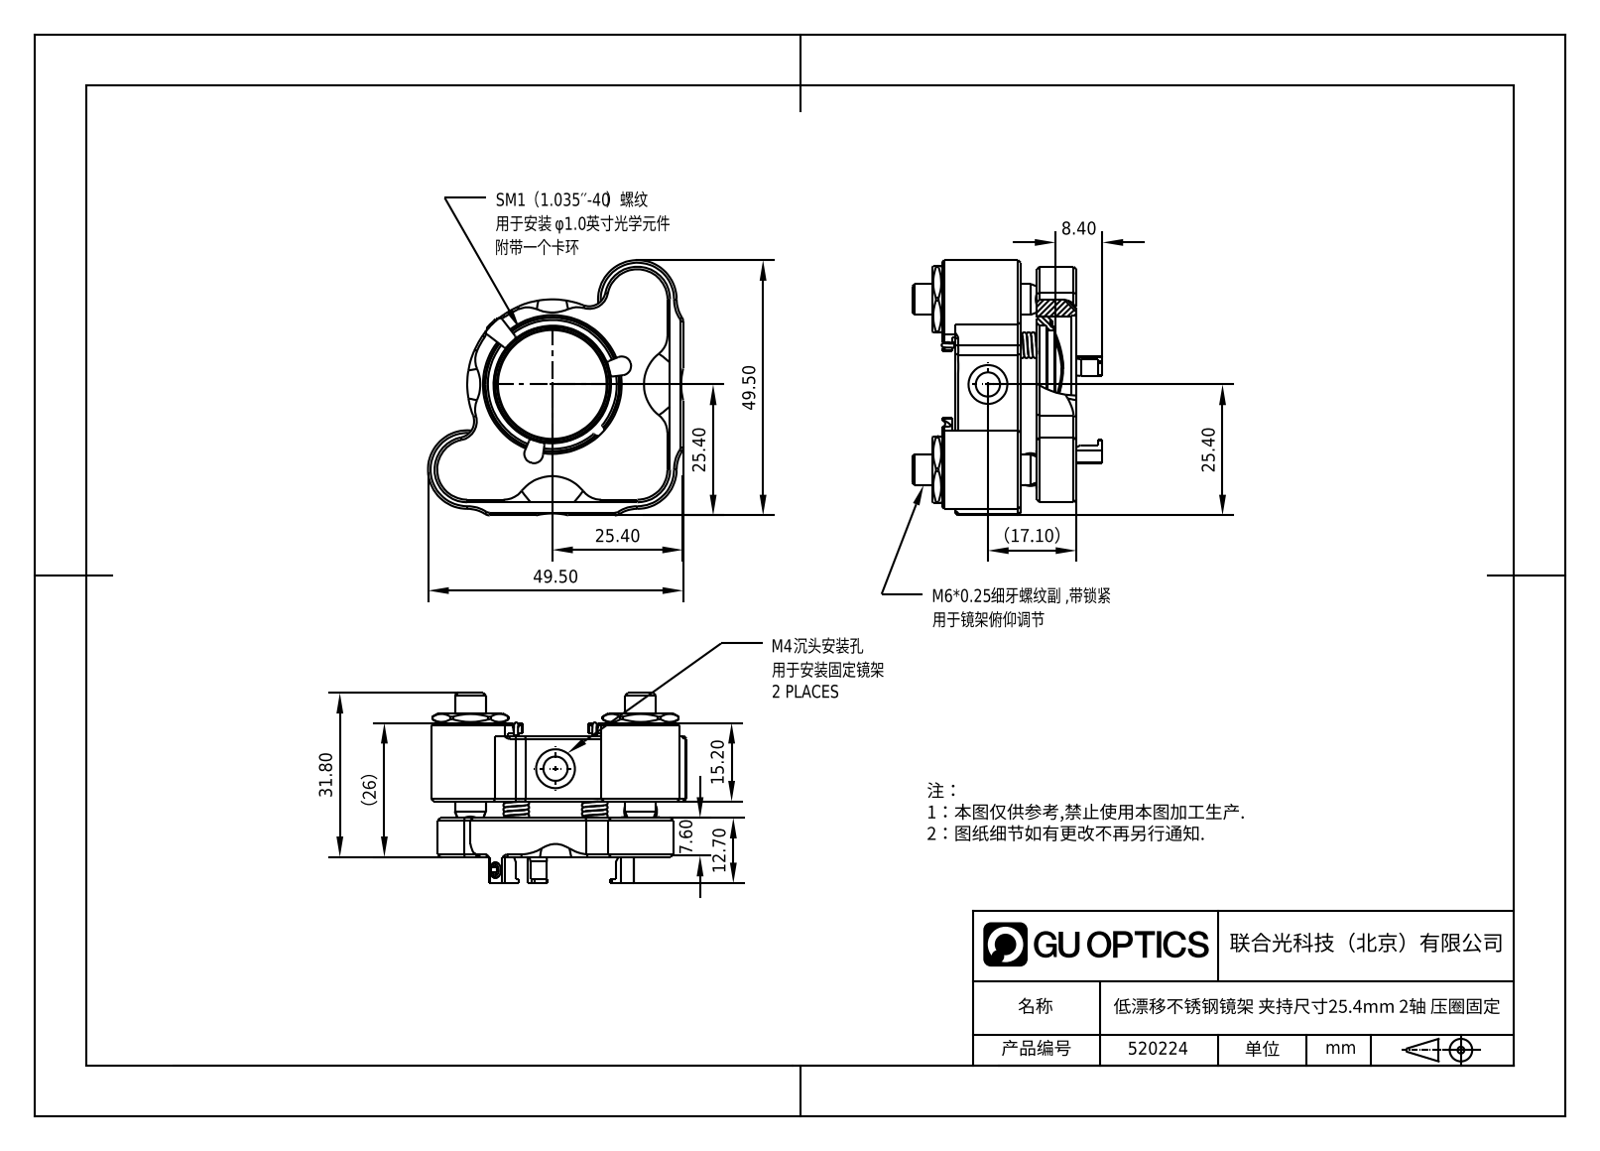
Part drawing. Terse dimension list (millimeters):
name: DXS-0625标准型细牙螺丝_3.2.2.16-DXS-0625-26.6; 1.1.20.26.1_替代进口不锈钢光学调整架前面板，低变形，SM1.0，含一个卡环，两轴; 标准细牙锁紧螺母，外六角_3.2.6.14_DXJ-S0625-1302; 1.1.20.26_ZJO-PSM1.0-2 (+4 more)
written by: SolidWorks 2021 (CONFIG_CONTROL_DESIGN)
unit: mm
bodies: 23 solids, 629 faces (178 planar, 175 cylindrical, 276 other)
size: 49.53 × 49.53 × 39.25
volume: 21 735 mm³; area: 16 502 mm²
holes: 6× ⌀6.35, 5× ⌀2.5, 2× ⌀2.01, 2× ⌀3.99, 2× ⌀4.7, 2× ⌀7.54, 1× ⌀2, 1× ⌀6, 1× ⌀23.89, 1× ⌀26.29, 1× ⌀26.92
bosses: 6× ⌀4, 2× ⌀15.24, 1× ⌀6, 1× ⌀3
rounds: 14× R6.48, 12× R0.6, 8× R0.51, 4× R1, 4× R1.78, 4× R1.93, 3× R6.35, 2× R1.59
face distances: 10.92, 2.54, 7.62, 3.3, 15.24, 26.16, 18.54, 12.7, 16, 23.62
hole spacings: 15.2, 15.24, 18.18, 5, 8.89, 13.41, 18.23, 23.35
